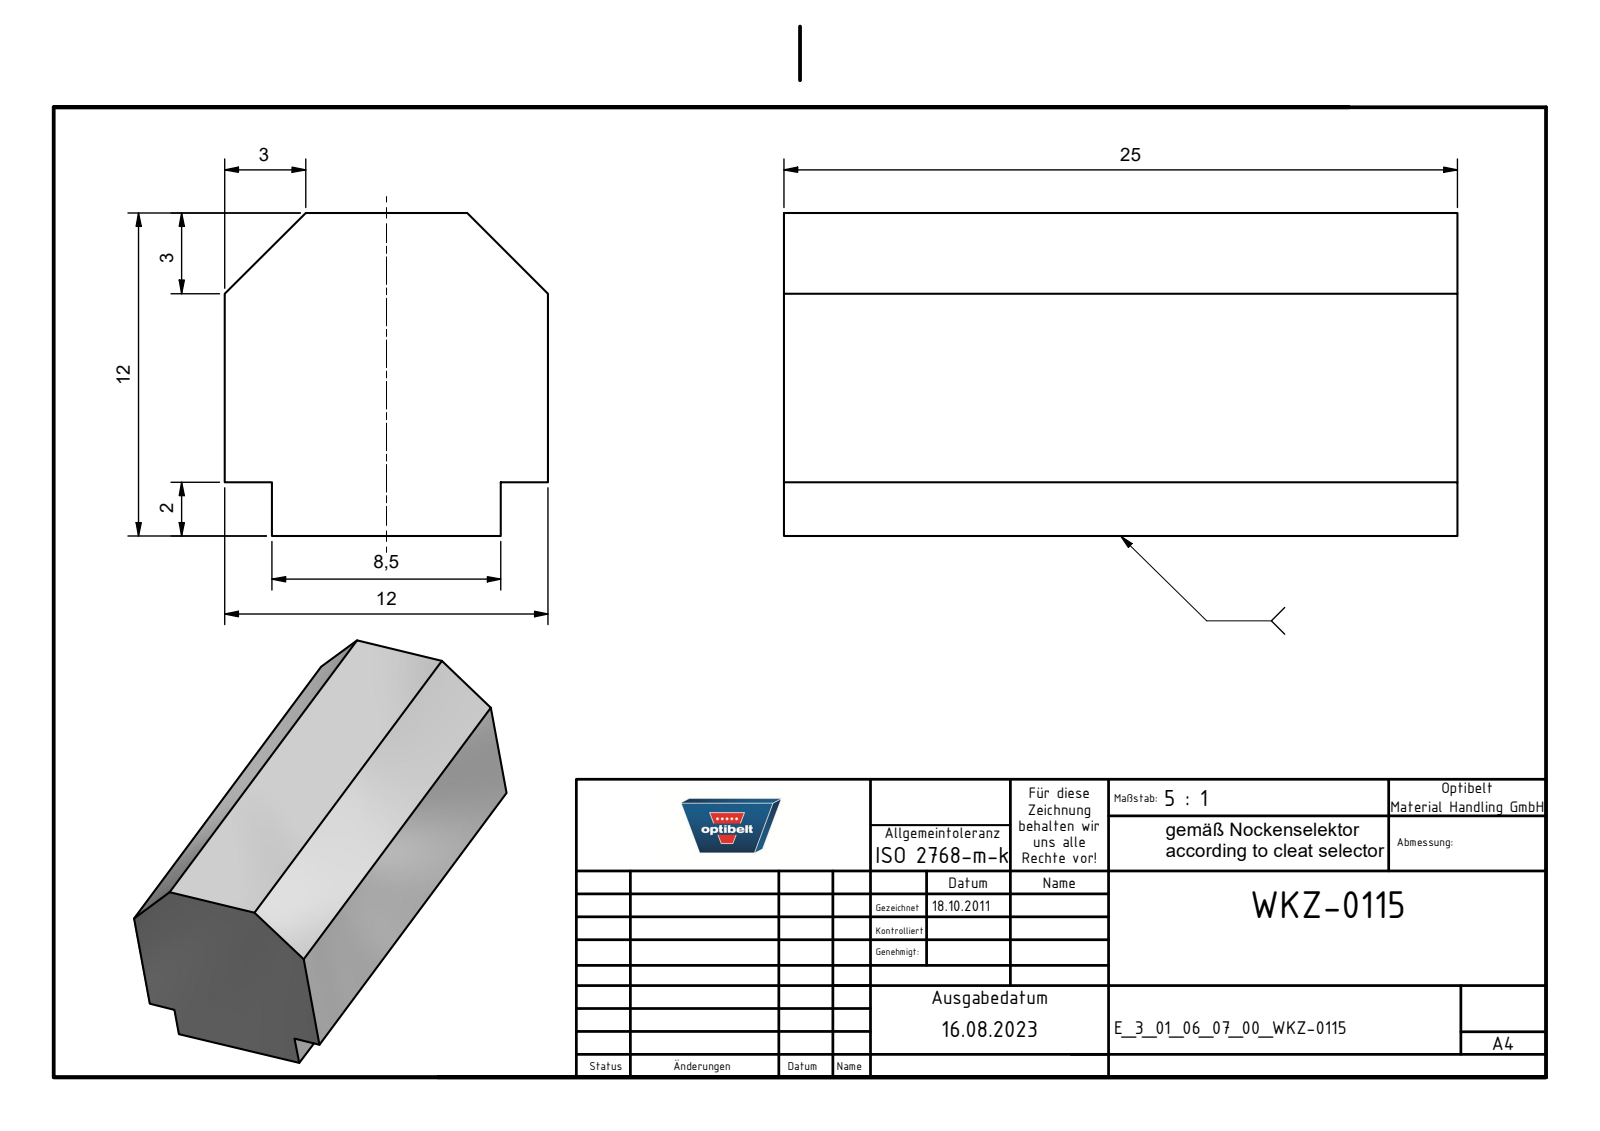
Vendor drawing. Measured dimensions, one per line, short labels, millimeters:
name: E_3_01_06_07_00_WKZ-0115
written by: Autodesk Inventor 2025 (AUTOMOTIVE_DESIGN)
unit: mm
bodies: 1 solid, 12 faces (12 planar, 0 cylindrical, 0 other)
size: 25 × 12 × 12
volume: 3 200 mm³; area: 1 368 mm²
face distances: 12, 25, 1.75, 10.25, 2, 10, 8.5
